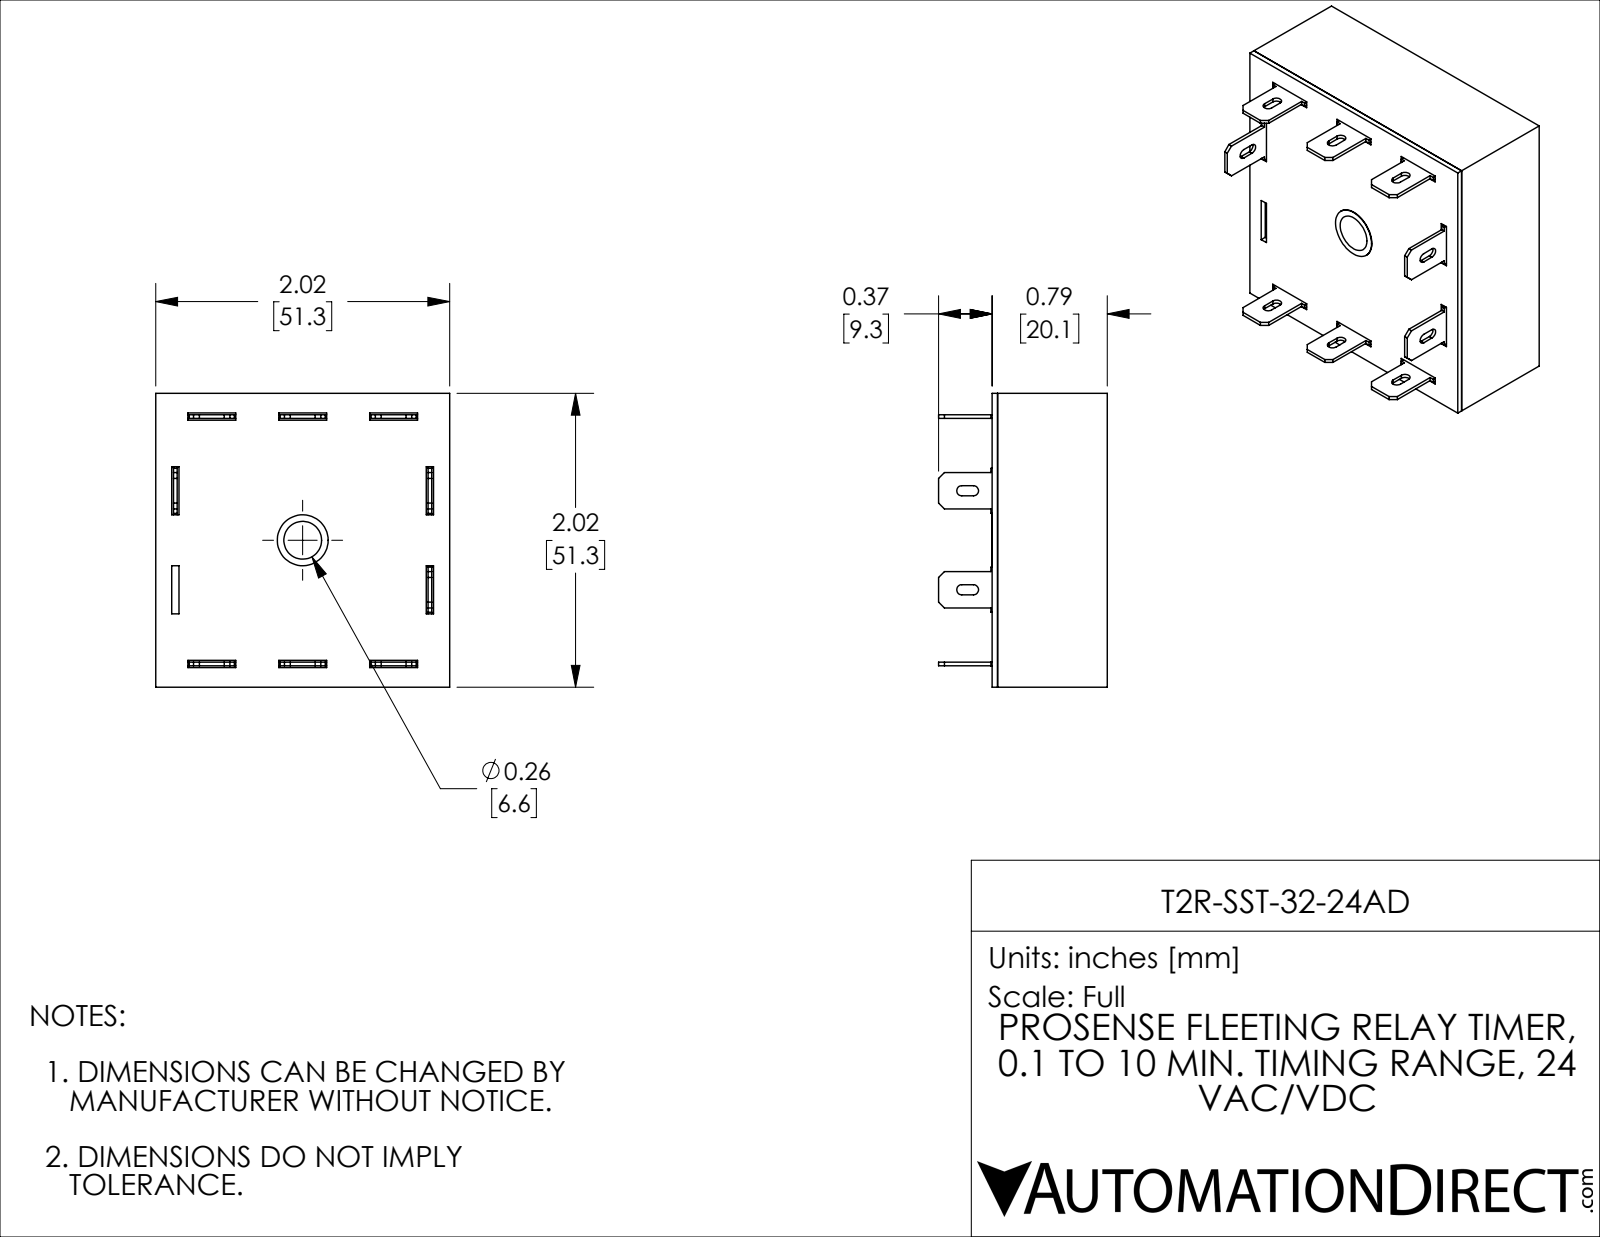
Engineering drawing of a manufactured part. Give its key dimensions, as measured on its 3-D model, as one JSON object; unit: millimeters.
{"part_name": "T2R-SST-32-24AD", "step_written_by": "SolidWorks 2021 (CONFIG_CONTROL_DESIGN)", "units": "millimeters", "bodies": {"solids": 11, "faces": 280, "planar": 256, "cylindrical": 22, "other": 2}, "overall_size": [51.31, 51.31, 29.46], "volume_mm3": 11178, "surface_area_mm2": 23301, "round_holes": [[8.89, 1]], "partial_cylinders_radius": [[0.89, 10]], "face_to_face_distances": [1.14, 50.16, 19.15, 20.12, 0.97, 18.01, 18.98, 51.3, 3.74, 47.56]}
